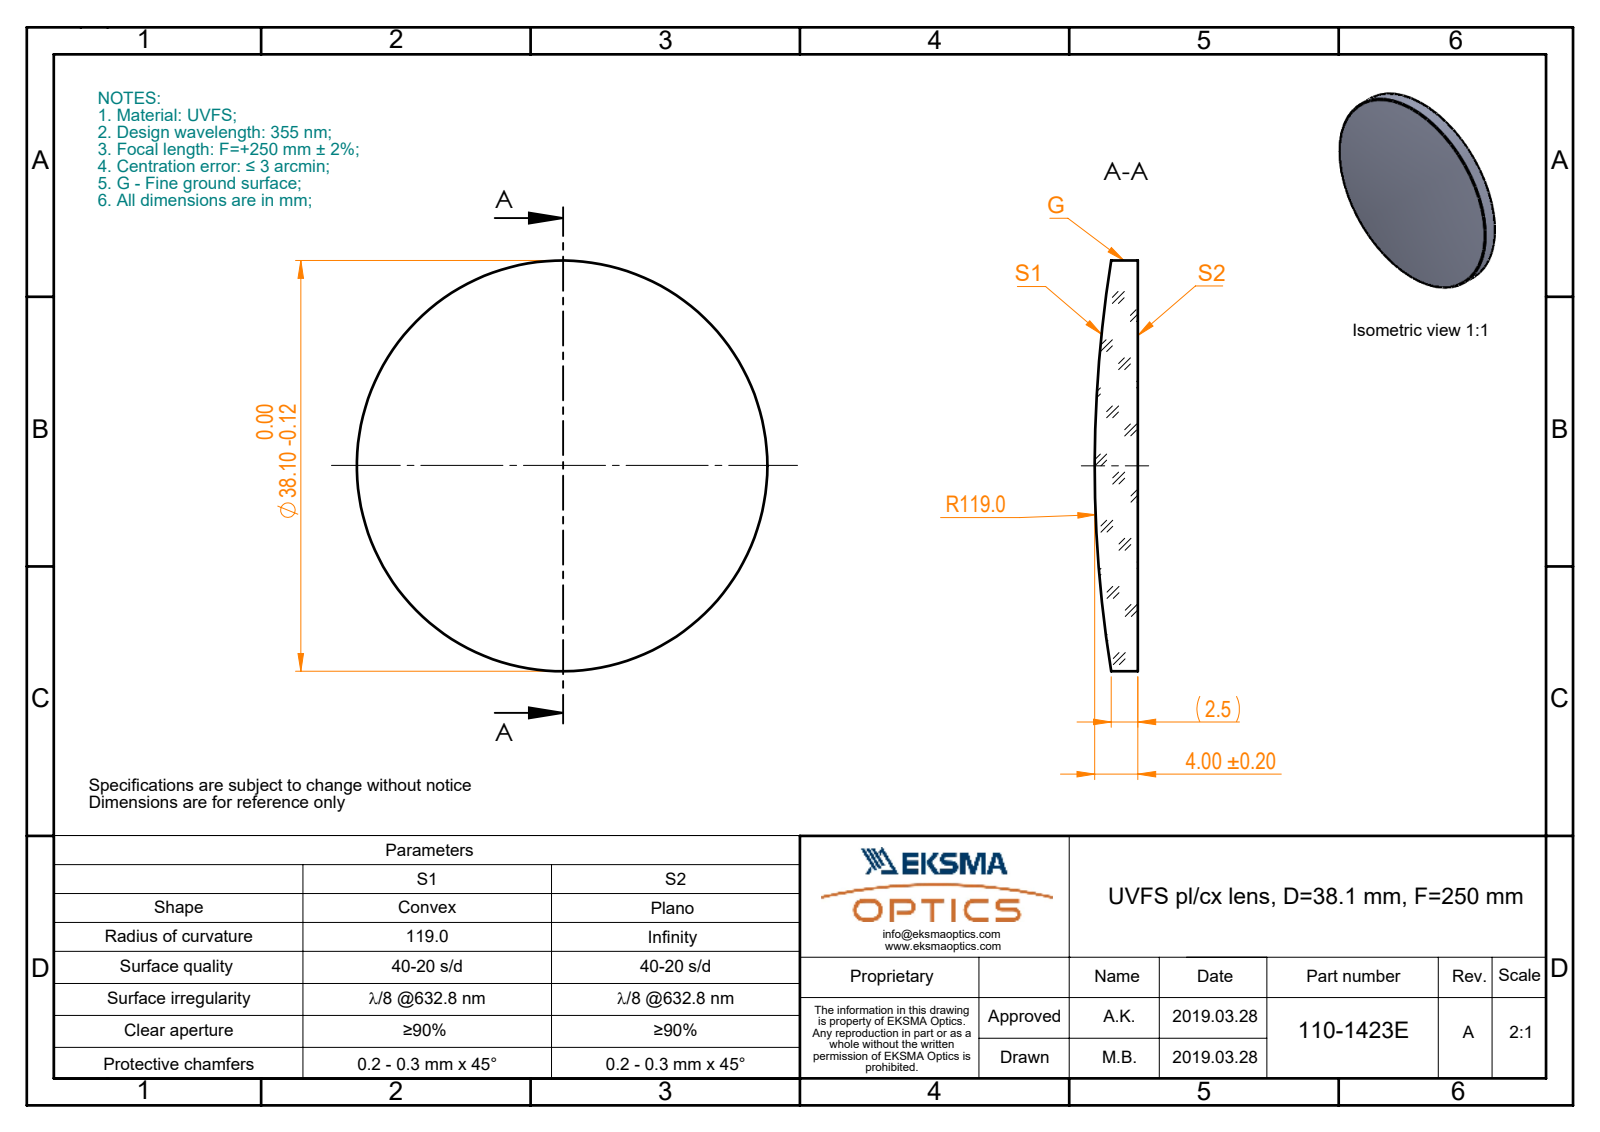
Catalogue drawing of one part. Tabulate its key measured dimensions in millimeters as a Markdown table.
| quantity | value |
| --- | --- |
| part name | 110-1423E UVFS pl-cx 38.1 F250 |
| STEP written by | SolidWorks 2017 (CONFIG_CONTROL_DESIGN) |
| units | millimeters |
| bodies | 1 solid, 5 faces (1 planar, 2 cylindrical, 2 other) |
| overall size | 38.1 × 38.1 × 4 |
| volume | 3 687 mm³ |
| surface area | 2 583 mm² |
| round bosses / shafts (diameter × count) | 38.1 × 1 |
